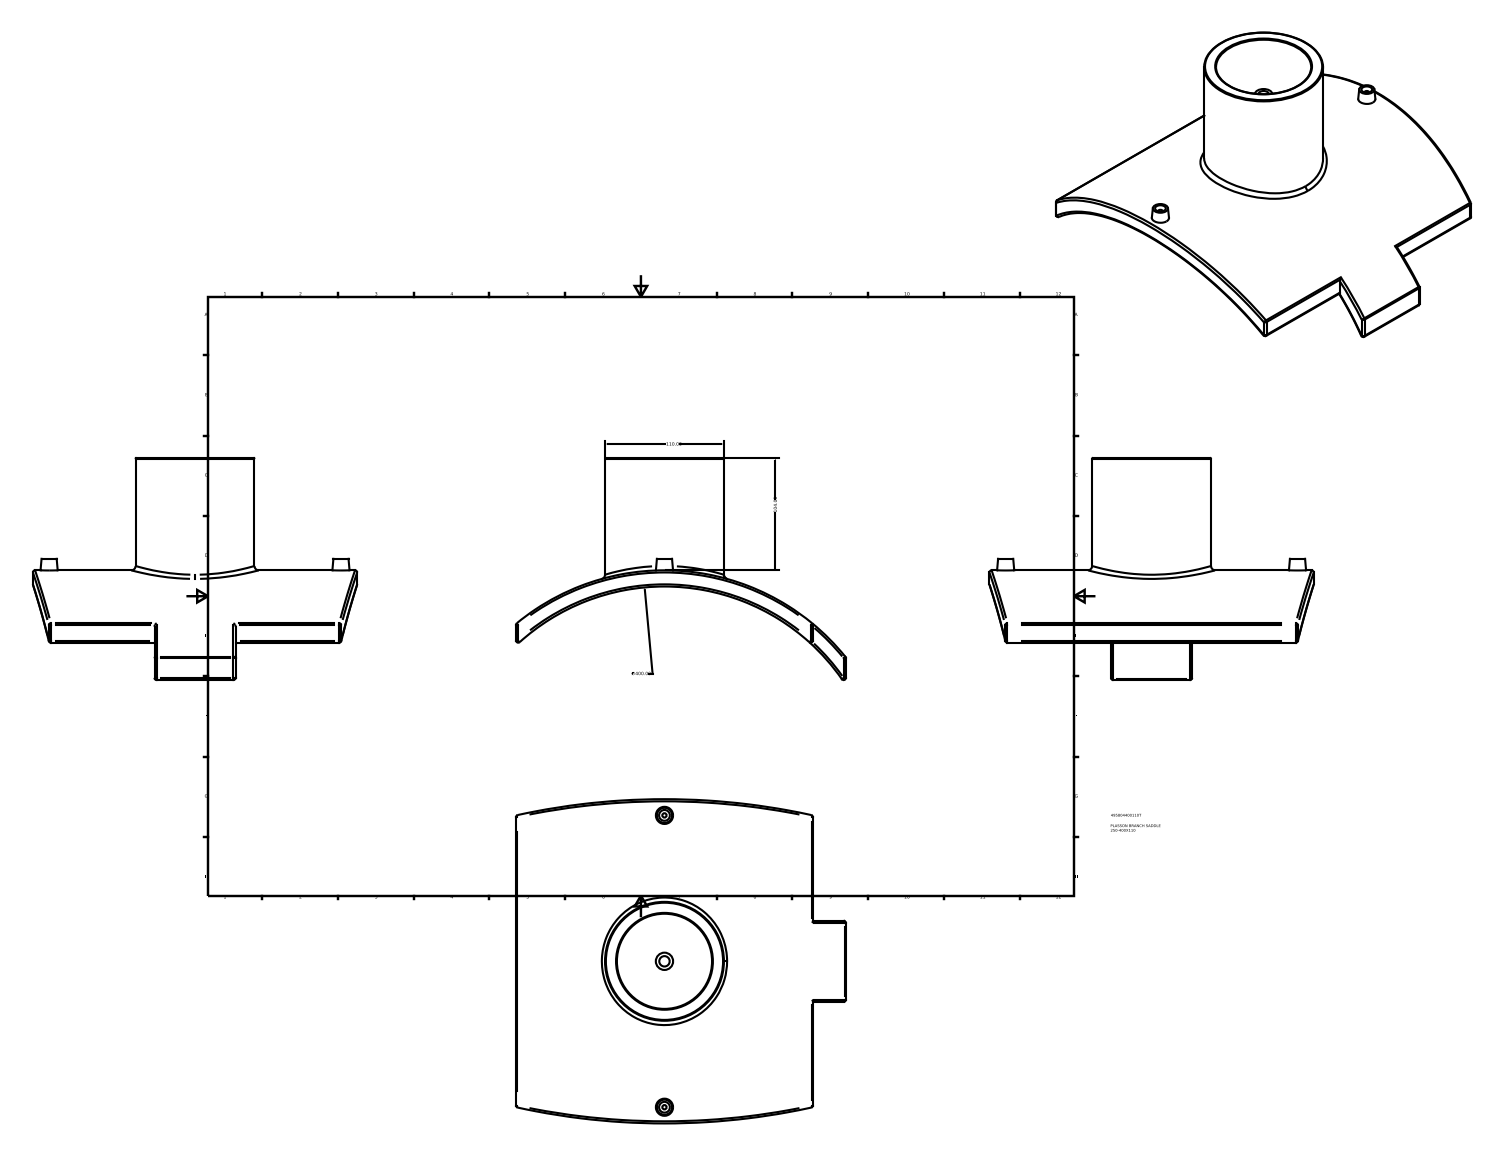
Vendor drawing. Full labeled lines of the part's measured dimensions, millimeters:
Part name (STEP PRODUCT): 495804400110T
STEP written by: Autodesk Inventor 2015 (AUTOMOTIVE_DESIGN)
Units: millimetres
Bodies: 1 solid, 66 faces (14 planar, 27 cylindrical, 25 other)
Overall size (bounding box): 305 × 300 × 205.54
Volume: 1 726 000 mm³ · Surface area: 272 190 mm²
Round holes (diameter × count): ⌀10 ×2, ⌀9.6 ×1, ⌀88 ×1
Round bosses / shafts (diameter × count): ⌀4 ×2, ⌀110 ×1, ⌀16 ×1
Partial cylindrical surfaces — rounded edges, fillets, slot ends (radius × count): R2 ×12, R635.42 ×2, R200 ×1, R215 ×1
Main face-to-face distances: 274.5, 305, 30.5, 75, 93.4, 14, 107.4, 76.2, 62.2, 31.2
Hole centre spacings: 135, 270
